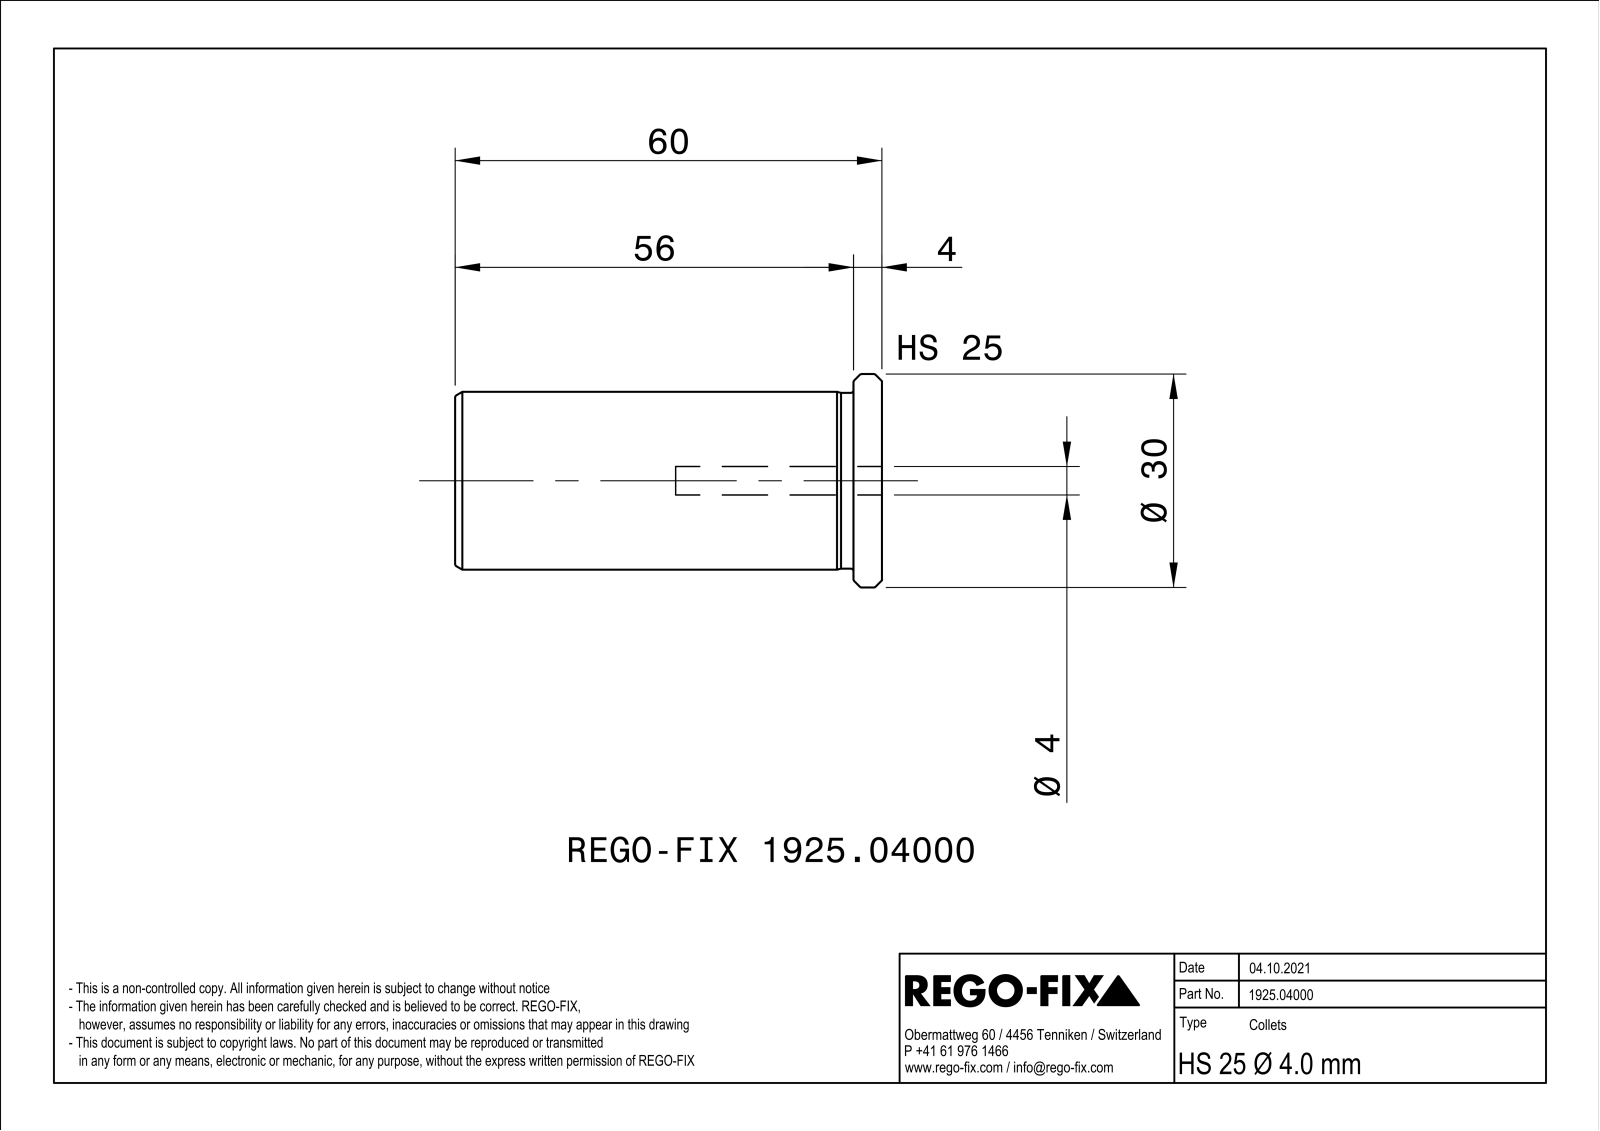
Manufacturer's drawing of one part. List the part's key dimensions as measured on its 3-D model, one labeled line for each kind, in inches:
Part name (STEP PRODUCT): NOCUT
STEP written by: SIEMENS PLM Software Solid Edge ST10 (AUTOMOTIVE_DESIGN)
Units: inches
Bodies: 1 solid, 73 faces (22 planar, 12 cylindrical, 39 other)
Overall size (bounding box): 2.362 × 1.181 × 1.181
Volume: 1.435 in³ · Surface area: 15.35 in²
Round holes (diameter × count): ⌀0.157 ×1, ⌀0.394 ×1, ⌀0.807 ×1
Round bosses / shafts (diameter × count): ⌀1.181 ×1, ⌀0.984 ×1, ⌀0.972 ×1
Main face-to-face distances: 0.031, 0.157, 2.362, 2.205
